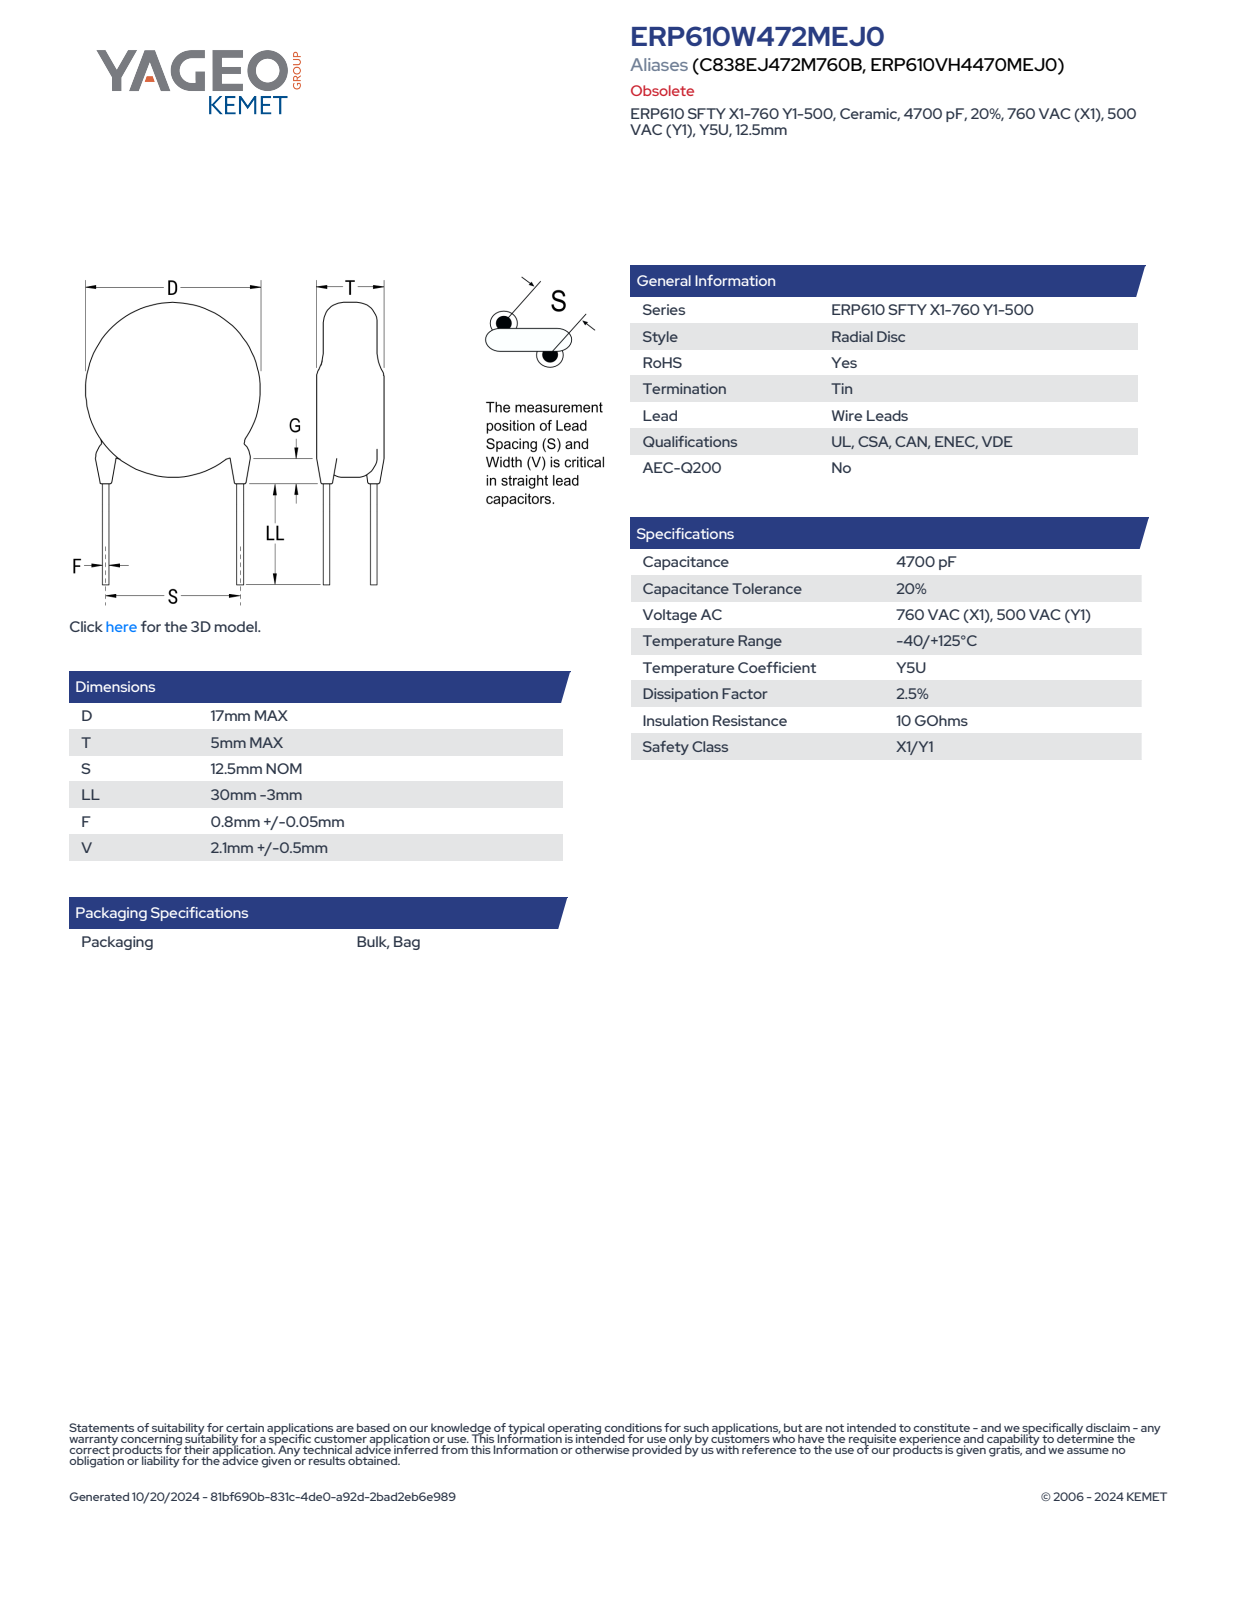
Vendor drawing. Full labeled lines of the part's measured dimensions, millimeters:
Part name (STEP PRODUCT): CCD_KST_17X5_D17T5S12.5LL27F0.85G3V2.6
STEP written by: SolidWorks 2014 (AUTOMOTIVE_DESIGN)
Units: millimetres
Bodies: 4 solids, 83 faces (61 planar, 10 cylindrical, 12 other)
Overall size (bounding box): 44.15 × 17 × 5
Volume: 1 146 mm³ · Surface area: 857 mm²
Round bosses / shafts (diameter × count): ⌀0.85 ×4, ⌀17 ×1
Main face-to-face distances: 5, 36.7, 34.59, 2.11, 0.52, 0.39, 6.27, 6.51, 35, 0.41
